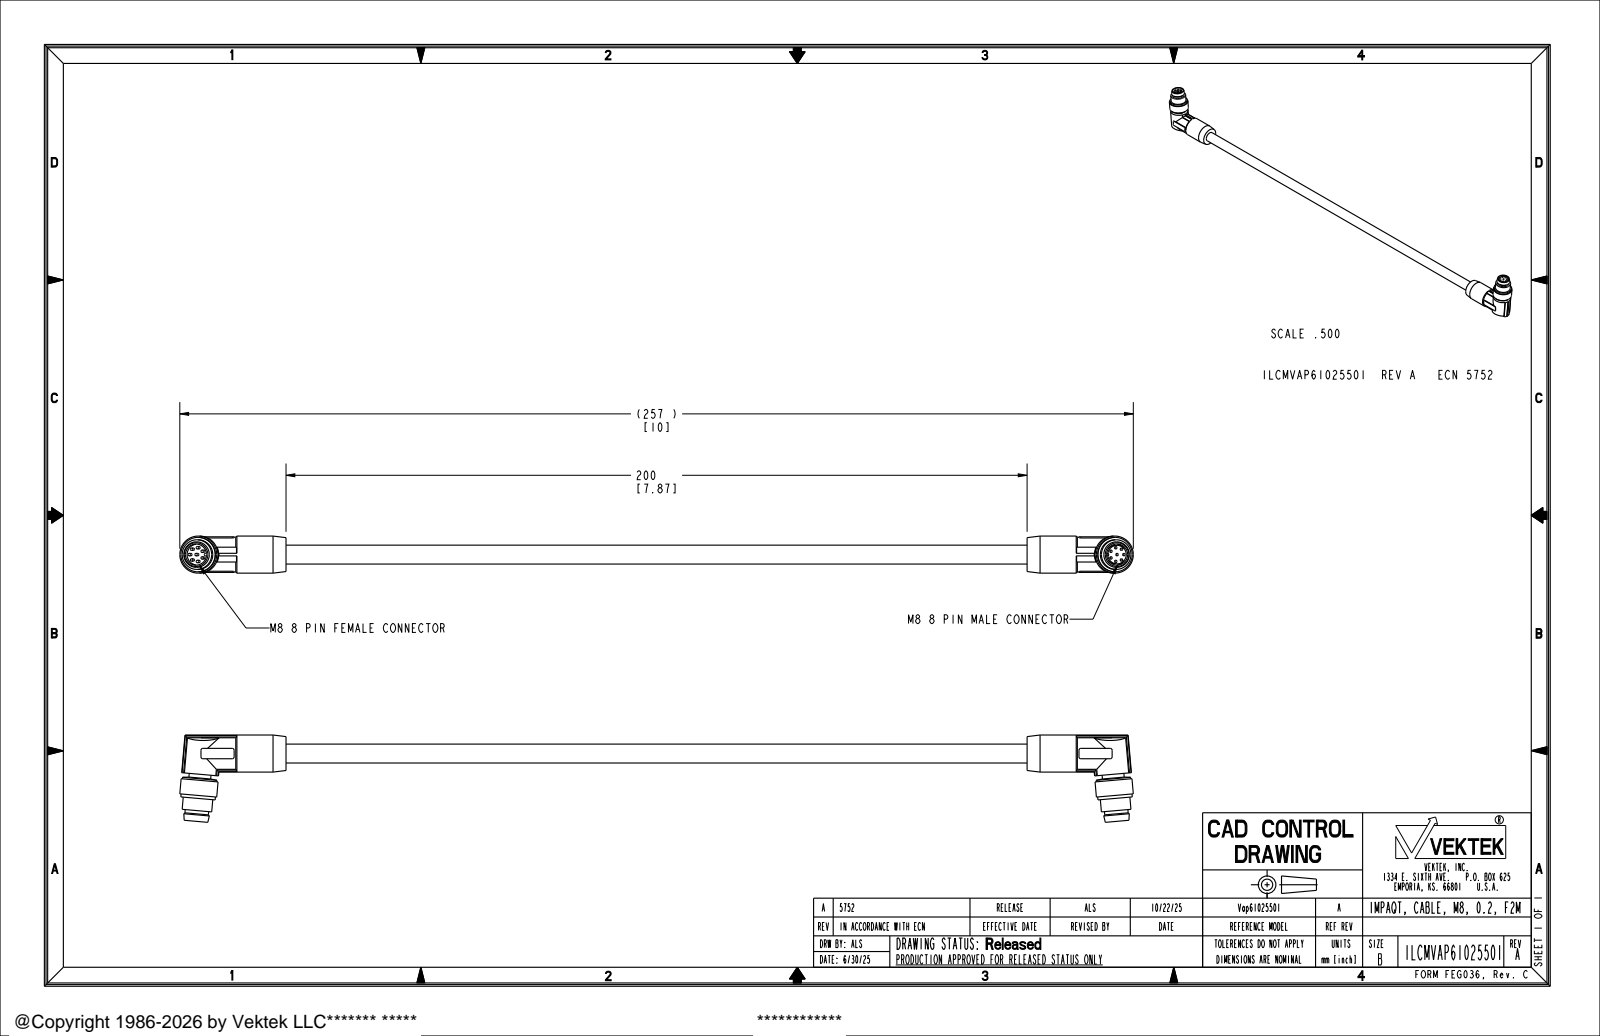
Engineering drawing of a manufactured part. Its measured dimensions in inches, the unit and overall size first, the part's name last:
Units: inches
Overall size (bounding box): 10.131 × 0.927 × 0.394
Round holes (diameter × count): ⌀0.026 ×8, ⌀0.224 ×2
Round bosses / shafts (diameter × count): ⌀0.026 ×8, ⌀0.394 ×3, ⌀0.366 ×3, ⌀0.315 ×2, ⌀0.25 ×2, ⌀0.232 ×2, ⌀0.201 ×1, ⌀0.197 ×1
Partial cylindrical surfaces — rounded edges, fillets, slot ends (radius × count): R0.02 ×8, R0.185 ×3, R0.193 ×3, R0.013 ×2
Main face-to-face distances: 0.378, 7.874, 0.161, 0.387, 0.11, 0.304, 0.083, 0.268, 0.323, 0.064
Hole centre spacings: 0.074, 0.114, 0.063, 0.063, 0.063, 0.074, 0.113, 0.12
Volume: 0.584 in³ · Surface area: 10.11 in²
Bodies: 1 solid, 218 faces (76 planar, 120 cylindrical, 22 other)
Part name (STEP PRODUCT): ILCMVAP61025501
STEP written by: CREO PARAMETRIC BY PTC INC, 2021164 (AUTOMOTIVE_DESIGN)
